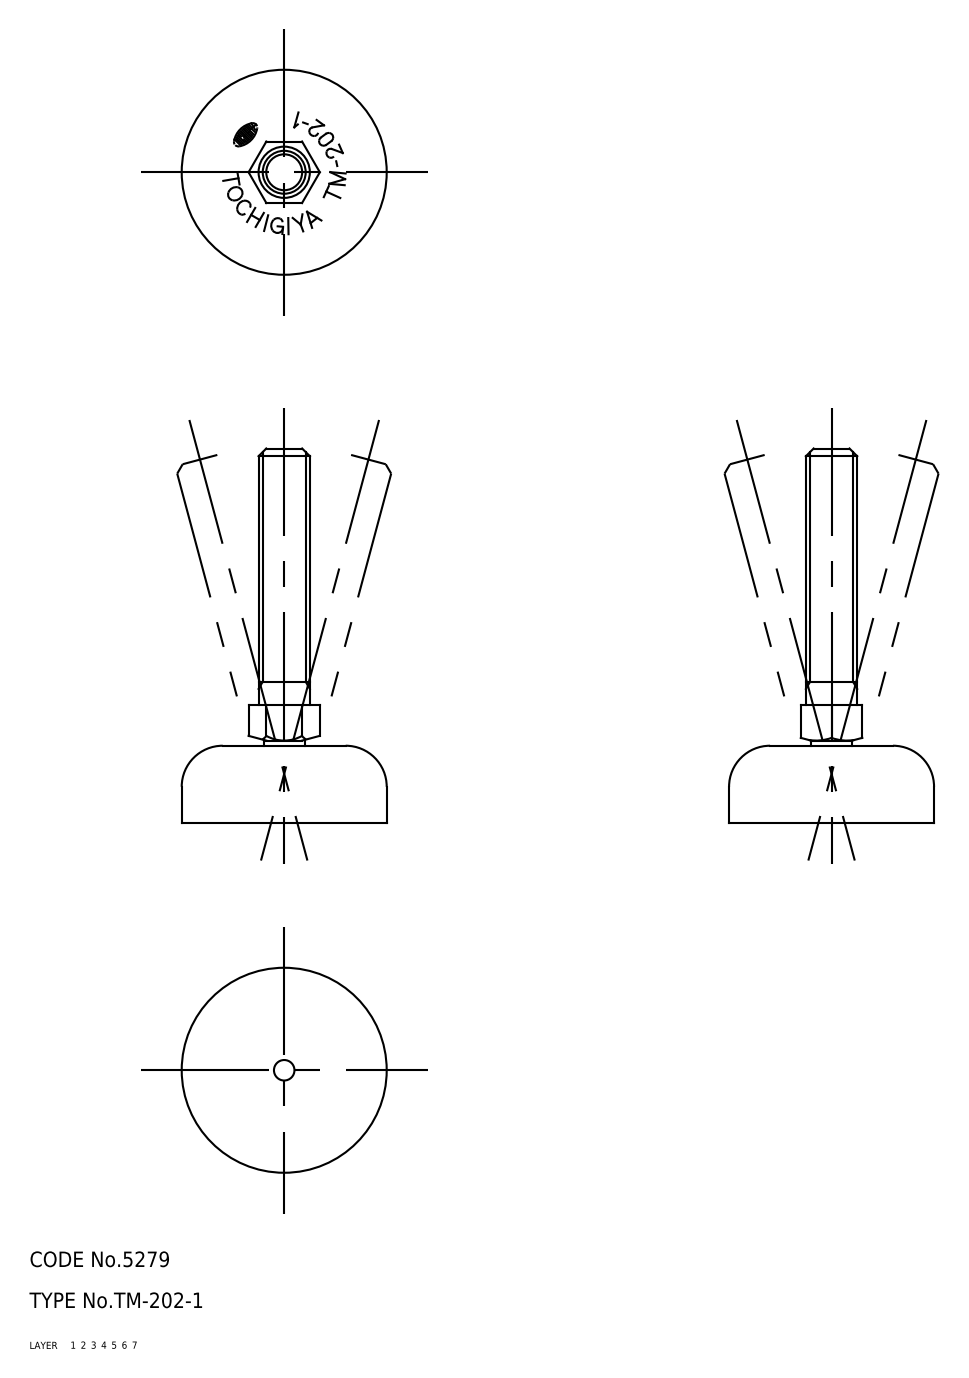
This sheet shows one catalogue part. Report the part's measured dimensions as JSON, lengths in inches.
{"part_name": "rubber pad; plate; bolt; TM_202_1_32741_36", "step_written_by": "CADfix (AUTOMOTIVE_DESIGN)", "units": "inches", "bodies": {"solids": 3, "faces": 56, "planar": 0, "cylindrical": 0, "other": 56}, "overall_size": [2.874, 1.575, 1.575], "volume_in3": 1.341, "surface_area_in2": 15.17}
